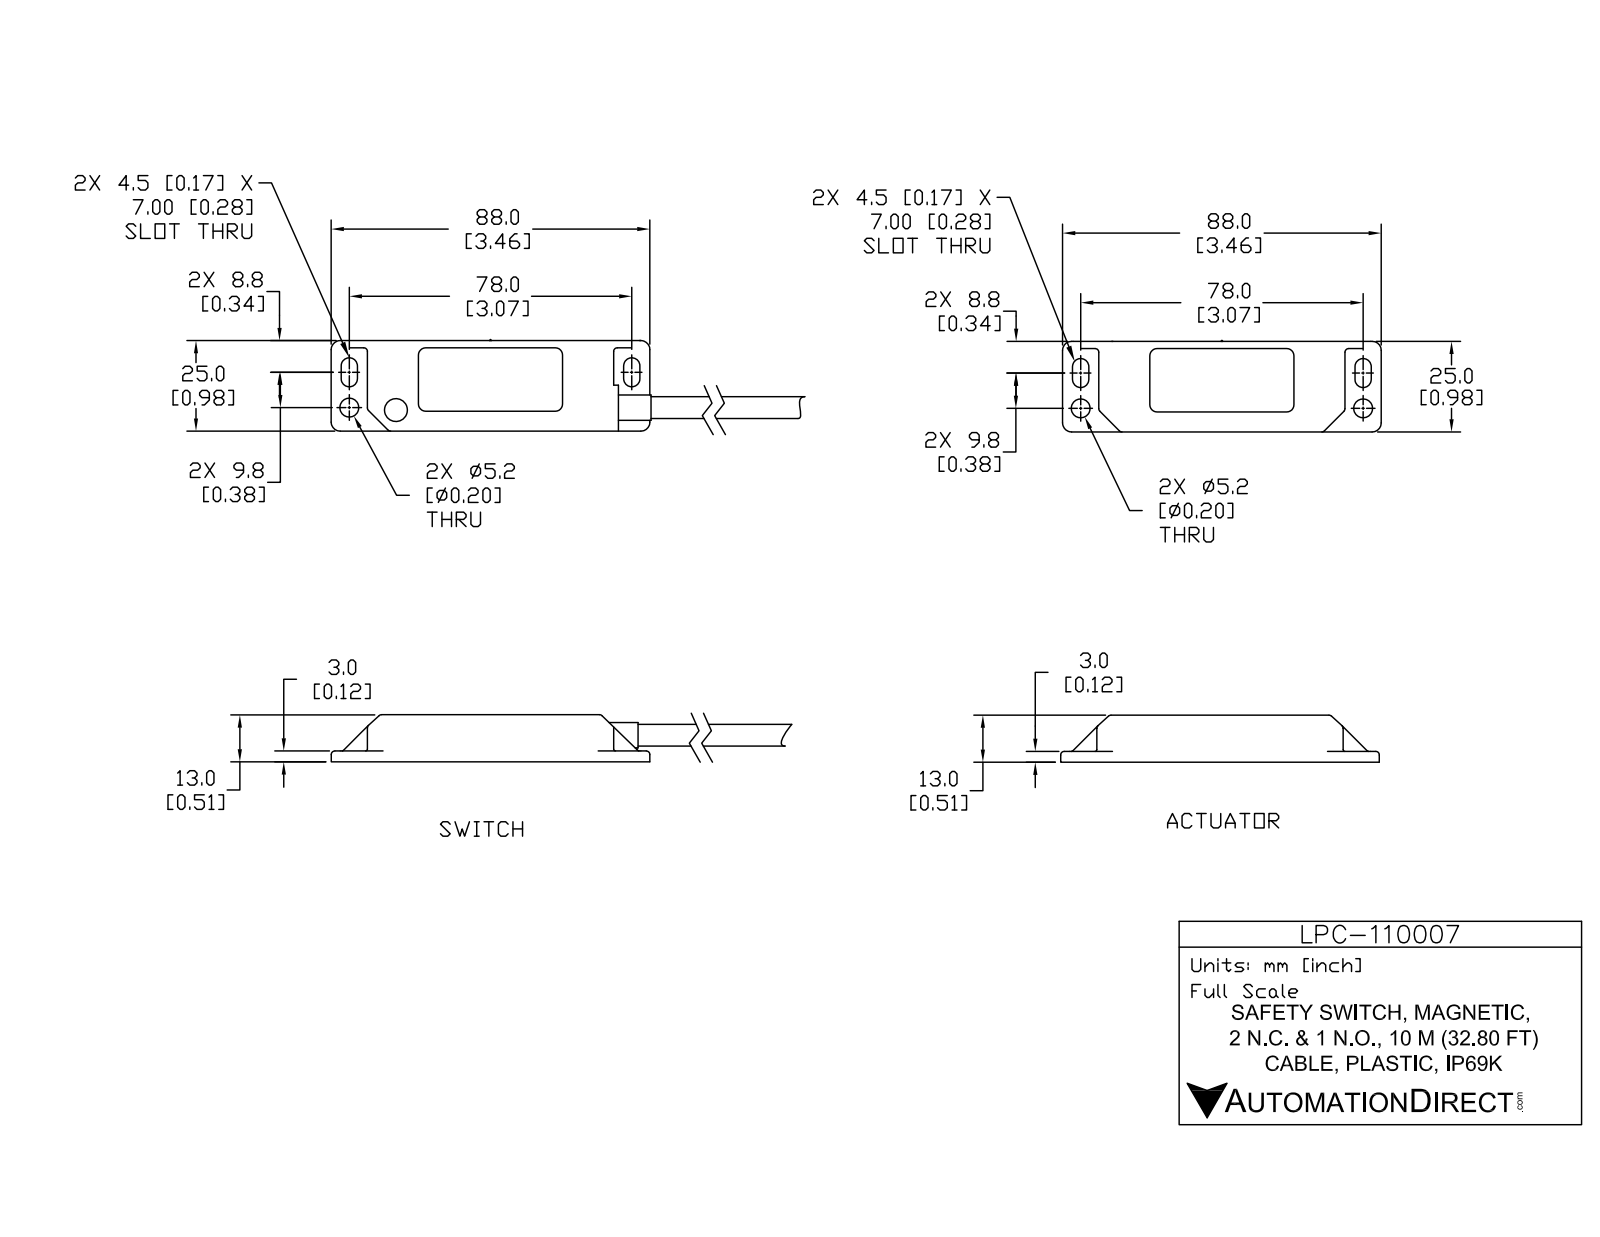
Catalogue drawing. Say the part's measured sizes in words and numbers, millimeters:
The part is named "LPC-110007; LPC-110007_2; LPC-110007_1". Its 3-D file was written by "SolidWorks 2017 (AUTOMOTIVE_DESIGN)". It is 11 solids with 1058 faces: 401 planar, 303 cylindrical and 354 other. Overall it measures 259.6 by 50.6 by 13.8 millimeters. Its volume is 27 830 cubic millimeters and its surface area 30 900 square millimeters. Round holes: 4 of diameter 5, 4 of diameter 5.2, 1 of diameter 3, 1 of diameter 4.4, 1 of diameter 5.4, 1 of diameter 5.9, 1 of diameter 7. Round bosses or shafts: 4 of diameter 2, 2 of diameter 4.9, 2 of diameter 2.3, 1 of diameter 8.6, 1 of diameter 7.6, 1 of diameter 7.1, 1 of diameter 6, 1 of diameter 5.3. Partial cylindrical surfaces (rounded edges, fillets, slot ends): 116 of radius 0.5, 49 of radius 1, 10 of radius 2, 8 of radius 2.3, 8 of radius 2.5, 6 of radius 0.3, 1 of radius 4.8. The main face-to-face distances are 1.7, 11.2, 2, 9.5, 1.5, 1.8, 12.9, 11.3, 13, 25.1. The hole center spacings are 19, 27.9, 30.2, 32.4, 37.6, 39.9, 45.3, 48.1.
